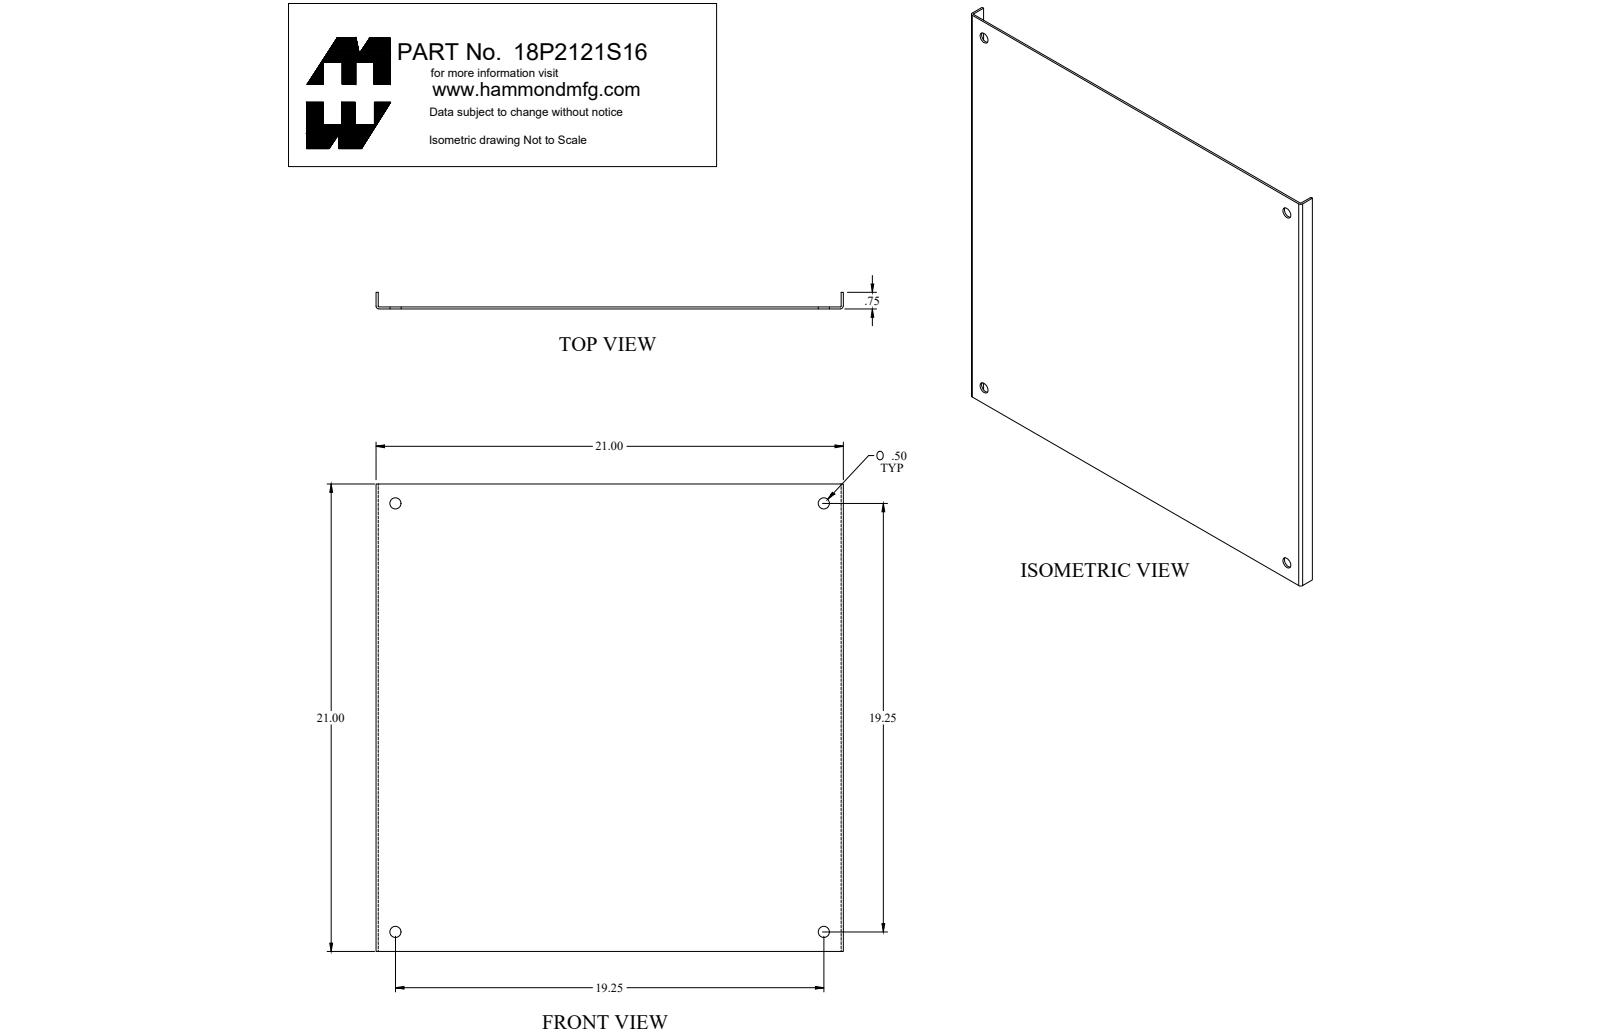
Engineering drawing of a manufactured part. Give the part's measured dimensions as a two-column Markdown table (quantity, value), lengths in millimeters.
| quantity | value |
| --- | --- |
| part name | 18P2121S16_Default |
| STEP written by | SolidWorks 2018 (CONFIG_CONTROL_DESIGN) |
| units | millimeters |
| bodies | 1 solid, 22 faces (10 planar, 12 cylindrical, 0 other) |
| overall size | 533.4 × 533.4 × 19.1 |
| volume | 725 900 mm³ |
| surface area | 607 400 mm² |
| round holes (diameter × count) | 12.7 × 4 |
| partial cylindrical surfaces (radius × count) | 0.8 × 2, 3.2 × 2 |
| main face-to-face distances | 2.4, 531, 533.4, 528.6, 19.1, 16.6 |
| hole center spacings | 489, 691.5 |
